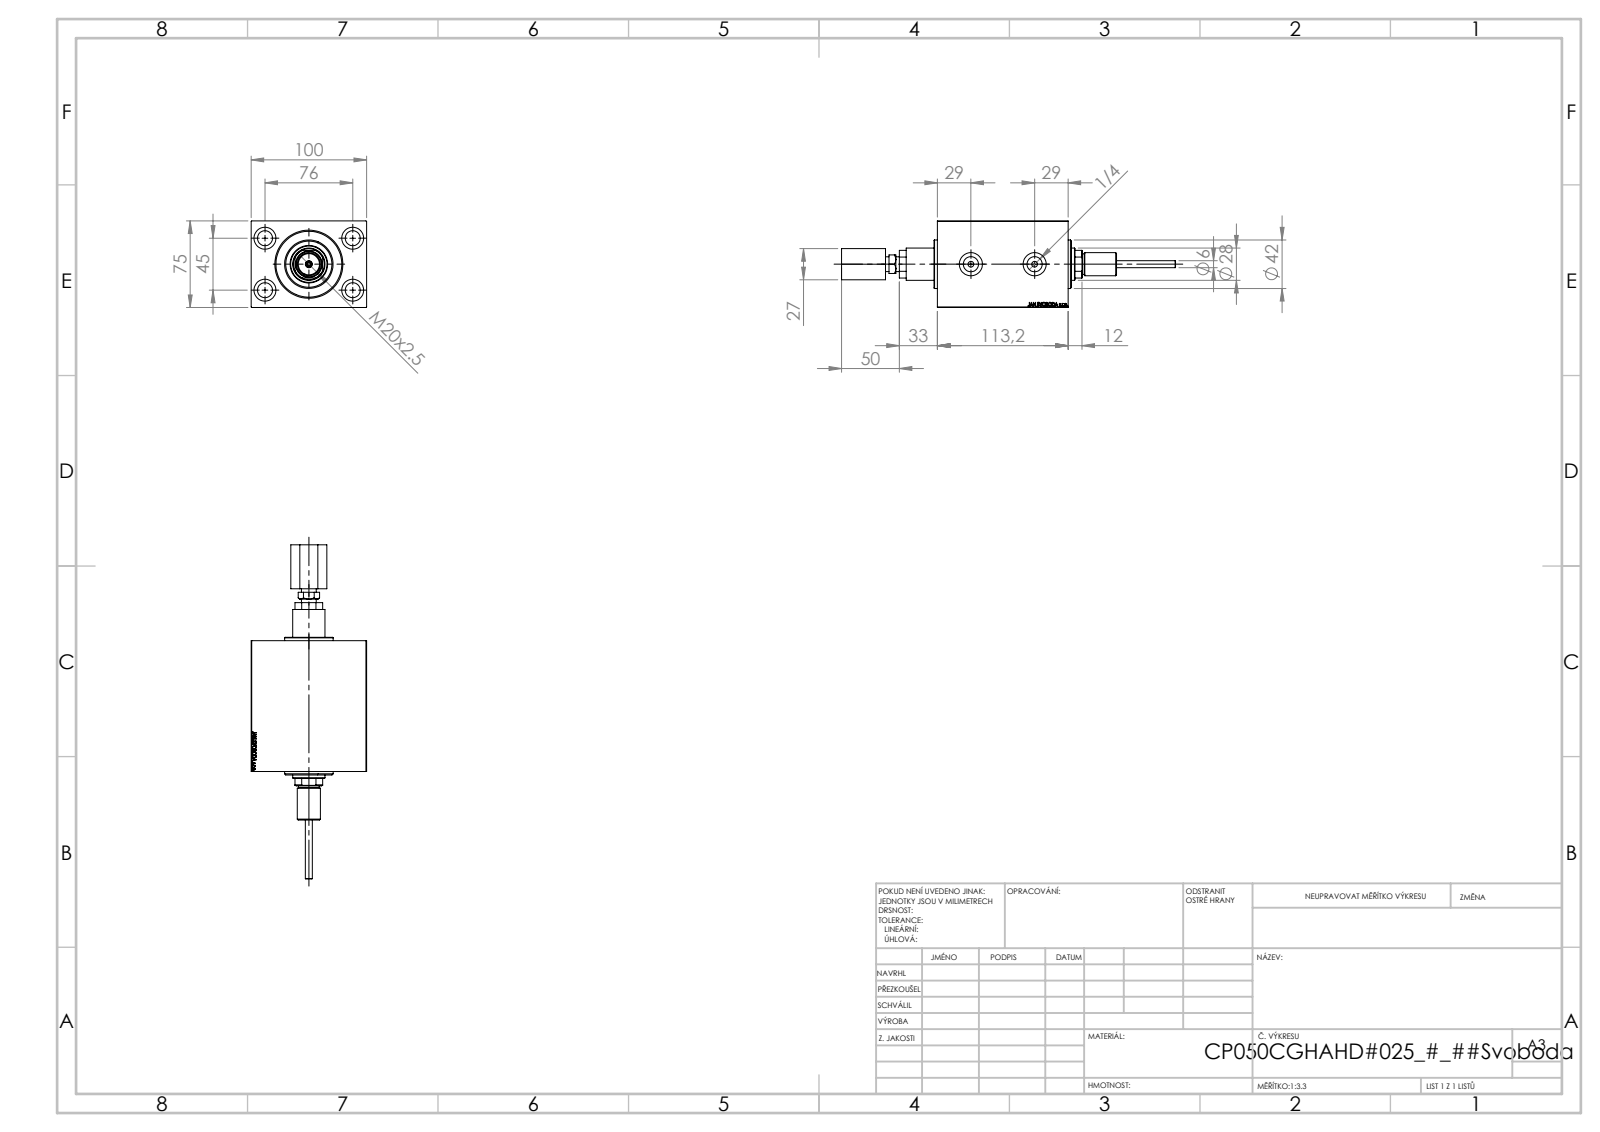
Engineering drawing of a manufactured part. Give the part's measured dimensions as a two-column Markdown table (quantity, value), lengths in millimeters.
| quantity | value |
| --- | --- |
| part name | V450DCP_B_RodCooling_ACCESSORIES; V450DCP_VC_B; V450DCP_C_Body; V450DCP_B_VCP (+1 more) |
| STEP written by | SolidWorks 2019 (CONFIG_CONTROL_DESIGN) |
| units | millimeters |
| bodies | 5 solids, 970 faces (446 planar, 106 cylindrical, 418 other) |
| overall size | 289.2 × 100 × 75 |
| volume | 792 664 mm³ |
| surface area | 145 930 mm² |
| round holes (diameter × count) | 13 × 4, 19 × 4, 4 × 2, 5 × 2, 9.73 × 2, 13.16 × 2, 15 × 2, 20 × 2, 3 × 1, 6 × 1, 18.5 × 1, 28 × 1 |
| round bosses / shafts (diameter × count) | 42 × 1, 20 × 1, 18 × 1, 12.78 × 1 |
| partial cylindrical surfaces (radius × count) | 13.5 × 1 |
| main face-to-face distances | 75, 100, 99.2, 113.2, 14, 13, 1, 112.2, 25, 55 |
| hole center spacings | 44.16, 45, 76, 88.32, 42.55, 55.2 |
